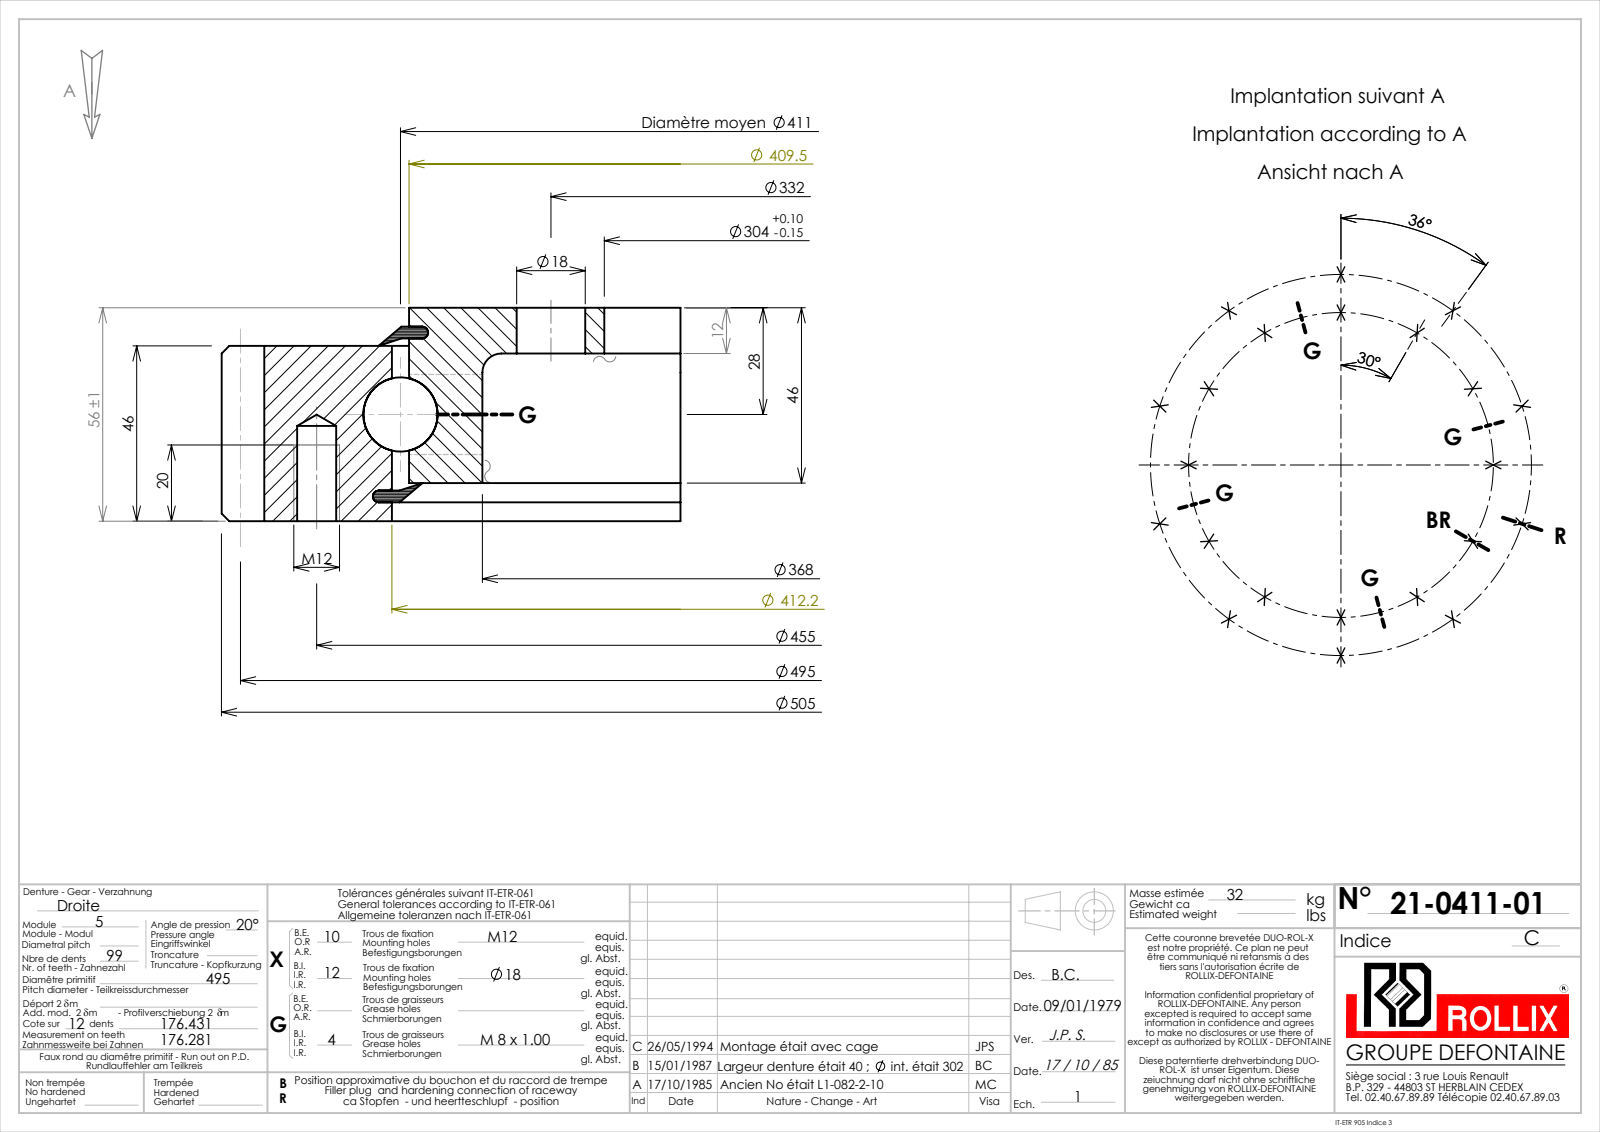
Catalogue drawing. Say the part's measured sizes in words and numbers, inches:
The part is named "21-0411-01". Its 3-D file was written by "SolidWorks 2016 (CONFIG_CONTROL_DESIGN)". It is 9 solids with 821 faces: 253 planar, 279 cylindrical and 289 other. Overall it measures 19.881 by 19.88 by 2.205 inches. Its volume is 234.2 cubic inches and its surface area 1 049 square inches. Round holes: 12 of diameter 0.709, 10 of diameter 0.404, 4 of diameter 0.276, 1 of diameter 11.969, 1 of diameter 14.488, 1 of diameter 16.228, 1 of diameter 16.358. Round bosses or shafts: 4 of diameter 0.315, 1 of diameter 16.122, 1 of diameter 16.004. Partial cylindrical surfaces (rounded edges, fillets, slot ends): 1 of radius 9.498, 1 of radius 9.941. The main face-to-face distances are 1.811, 0.394, 2.205, 1.417, 1.732, 1.339, 0.079, 0.472, 0.317, 1.888. The hole center spacings are 6.535, 3.383, 9.243, 11.32, 12.626, 8.957, 17.037, 5.535.
